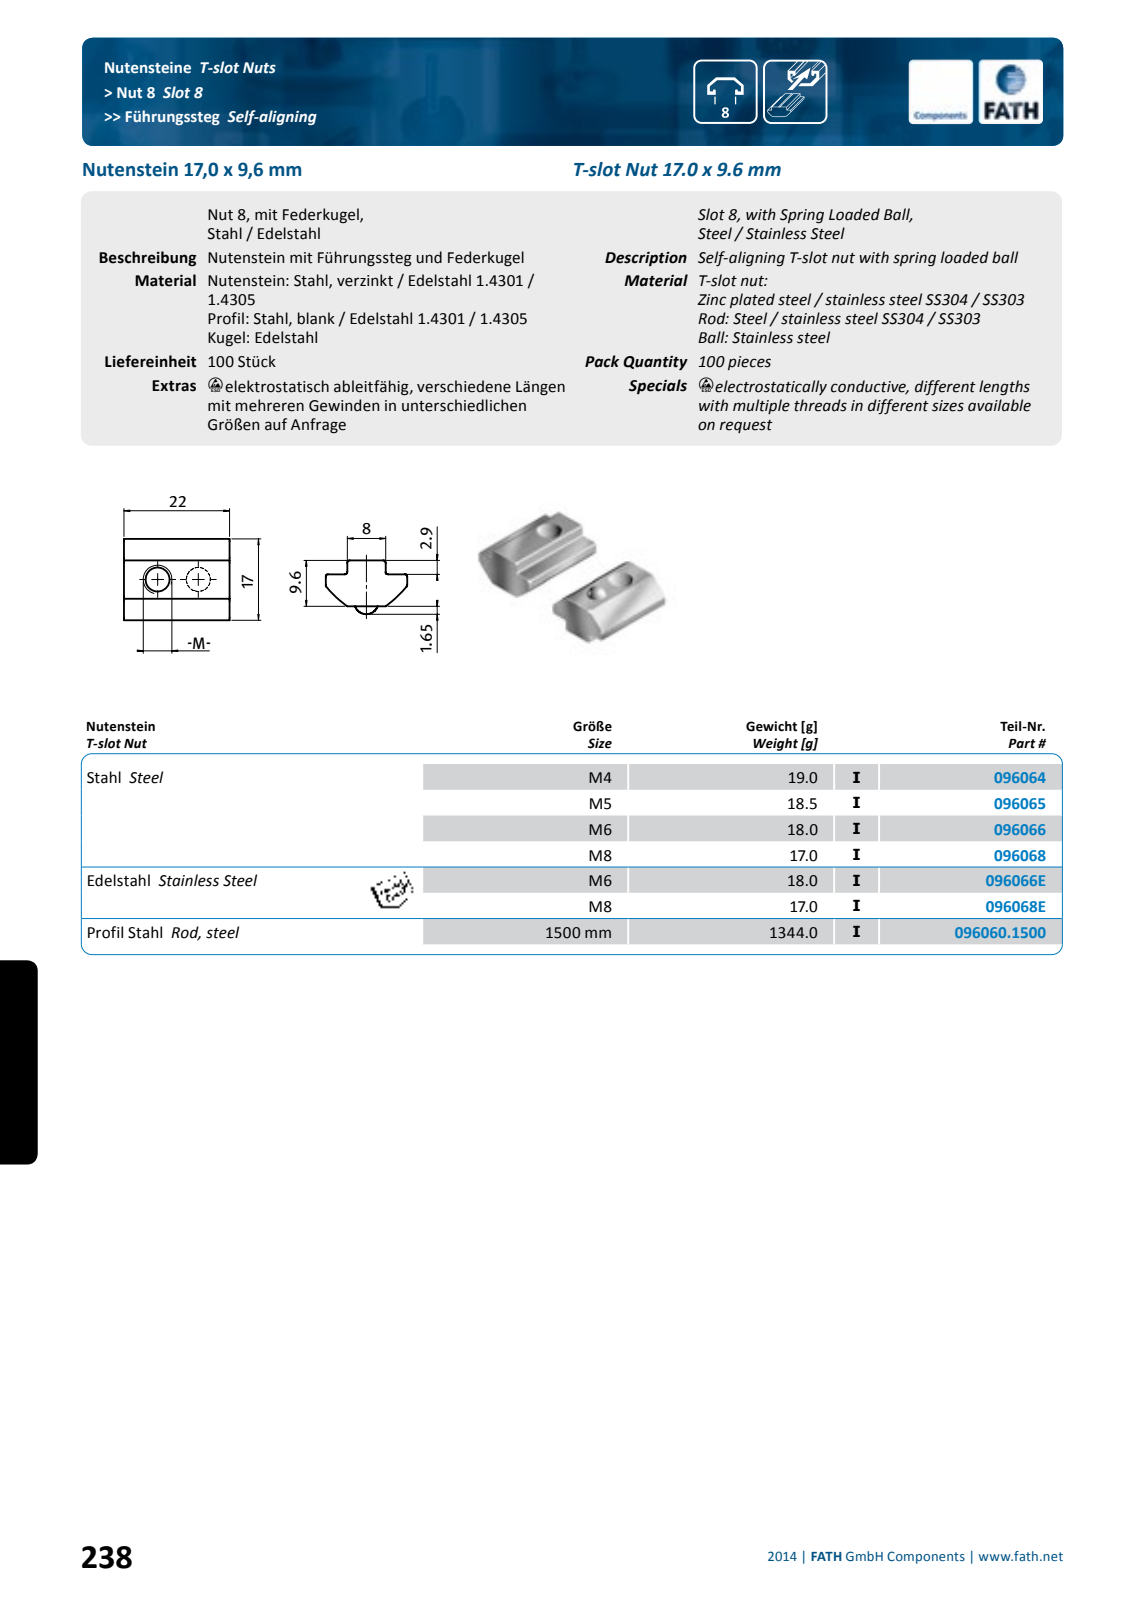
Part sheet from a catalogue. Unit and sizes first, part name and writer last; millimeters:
Units: millimetres
Overall size (bounding box): 22 × 17 × 11.4
Round holes (diameter × count): ⌀5 ×1, ⌀6.8 ×1
Partial cylindrical surfaces — rounded edges, fillets, slot ends (radius × count): R0.5 ×8, R24.5 ×2
Main face-to-face distances: 6.7, 22, 9.6, 2.9, 4.55, 12.45, 17, 7.9, 5.75, 9.25
Hole centre spacings: 8.5
Volume: 2 199 mm³ · Surface area: 1 606 mm²
Bodies: 3 solids, 54 faces (20 planar, 18 cylindrical, 16 other)
Part name (STEP PRODUCT): fath_096068_1; fath_096068_2; fath_096068_3
STEP written by: Spatial InterOp 3D (automotive_design)
